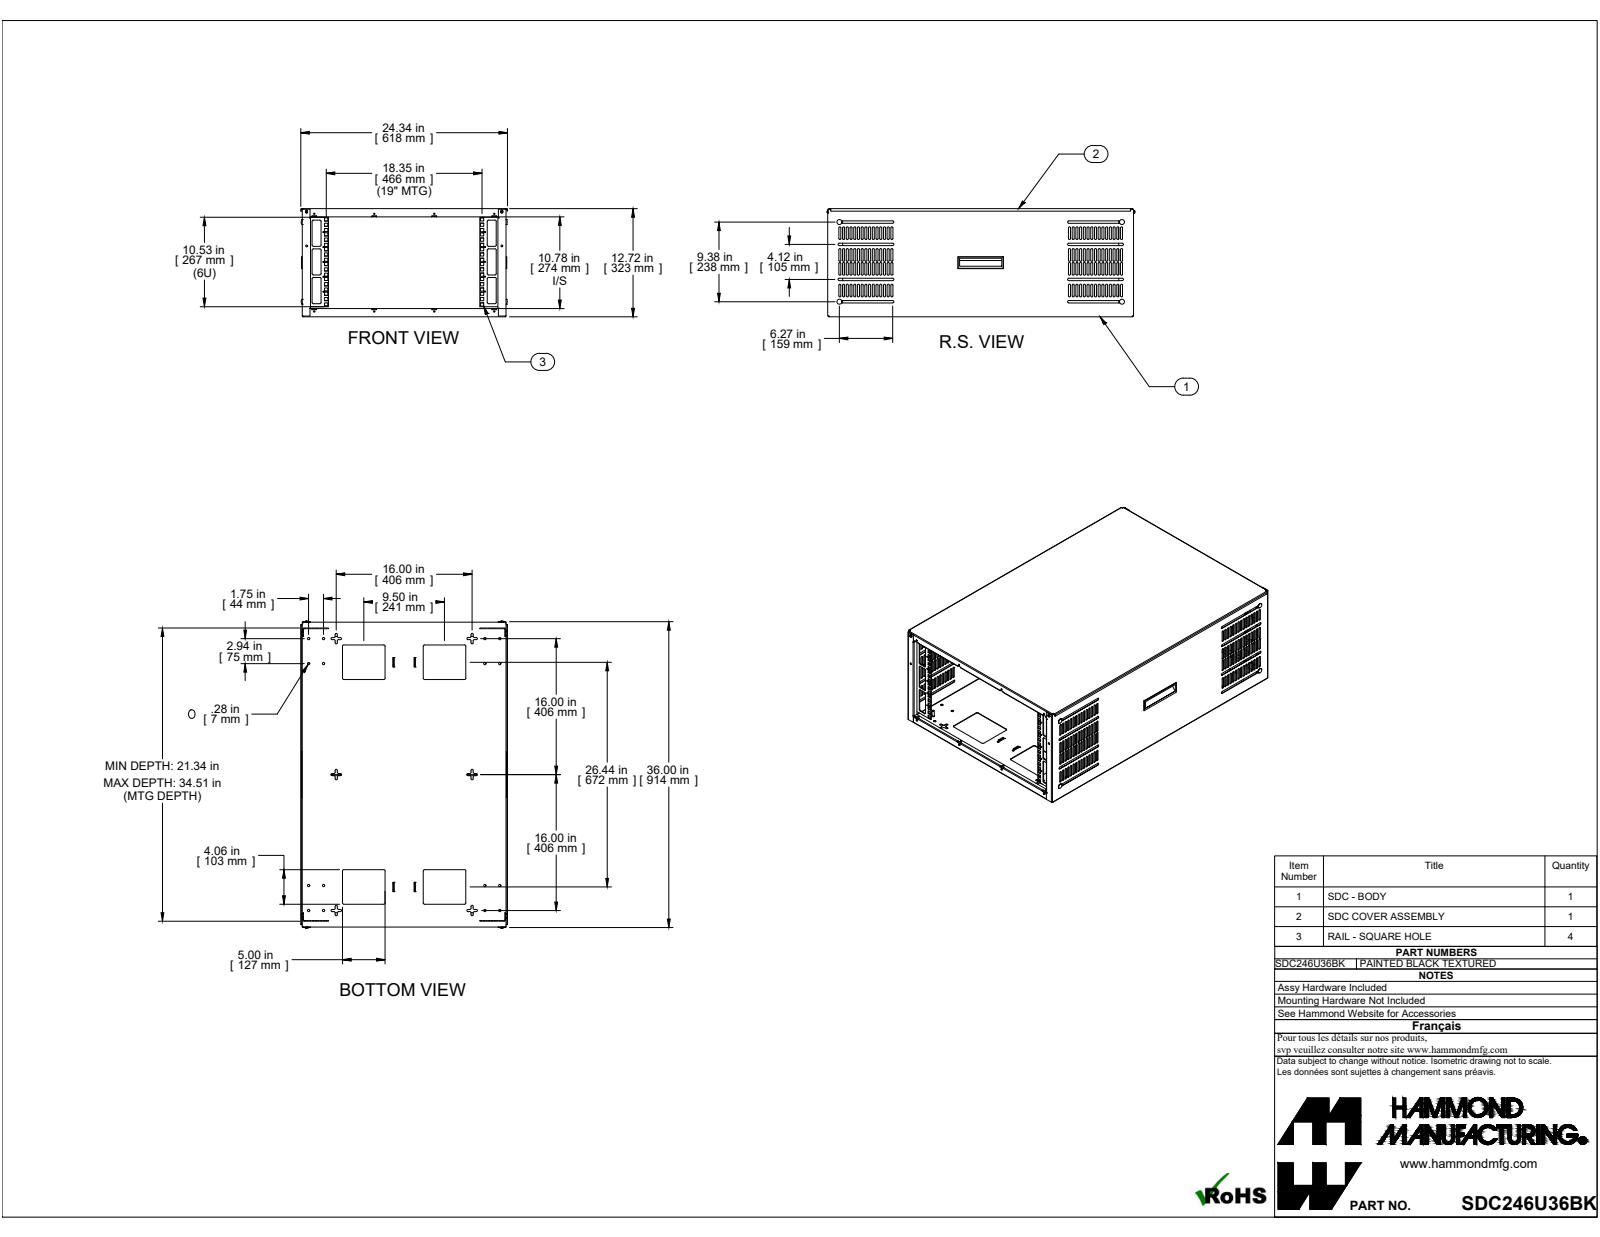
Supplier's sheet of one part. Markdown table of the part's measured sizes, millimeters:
| quantity | value |
| --- | --- |
| part name | SDC246U36BK |
| STEP written by | SolidWorks 2019 (CONFIG_CONTROL_DESIGN) |
| units | millimeters |
| bodies | 37 solids, 2664 faces (1654 planar, 958 cylindrical, 52 other) |
| overall size | 918.7 × 618.3 × 323.1 |
| volume | 2 822 000 mm³ |
| surface area | 3 819 000 mm² |
| round holes (diameter × count) | 3.2 × 20, 4.3 × 16, 7.1 × 16, 5 × 4, 4 × 2, 4.7 × 2, 5.4 × 2 |
| round bosses / shafts (diameter × count) | 6.4 × 8, 14.7 × 4, 8 × 2, 7.1 × 2, 4.7 × 2, 3.5 × 2 |
| partial cylindrical surfaces (radius × count) | 3 × 240, 4 × 68, 3.2 × 24, 0.7 × 22, 2.2 × 22, 0.6 × 16, 3.6 × 16, 3 × 14 |
| main face-to-face distances | 1.4, 321.7, 608.2, 320.2, 323.1, 606.7, 609.6, 1.8, 23.2, 319.9 |
| hole center spacings | 484.8, 44.5, 482.7, 490.8, 88.9, 74.6, 86.8, 179.4 |
